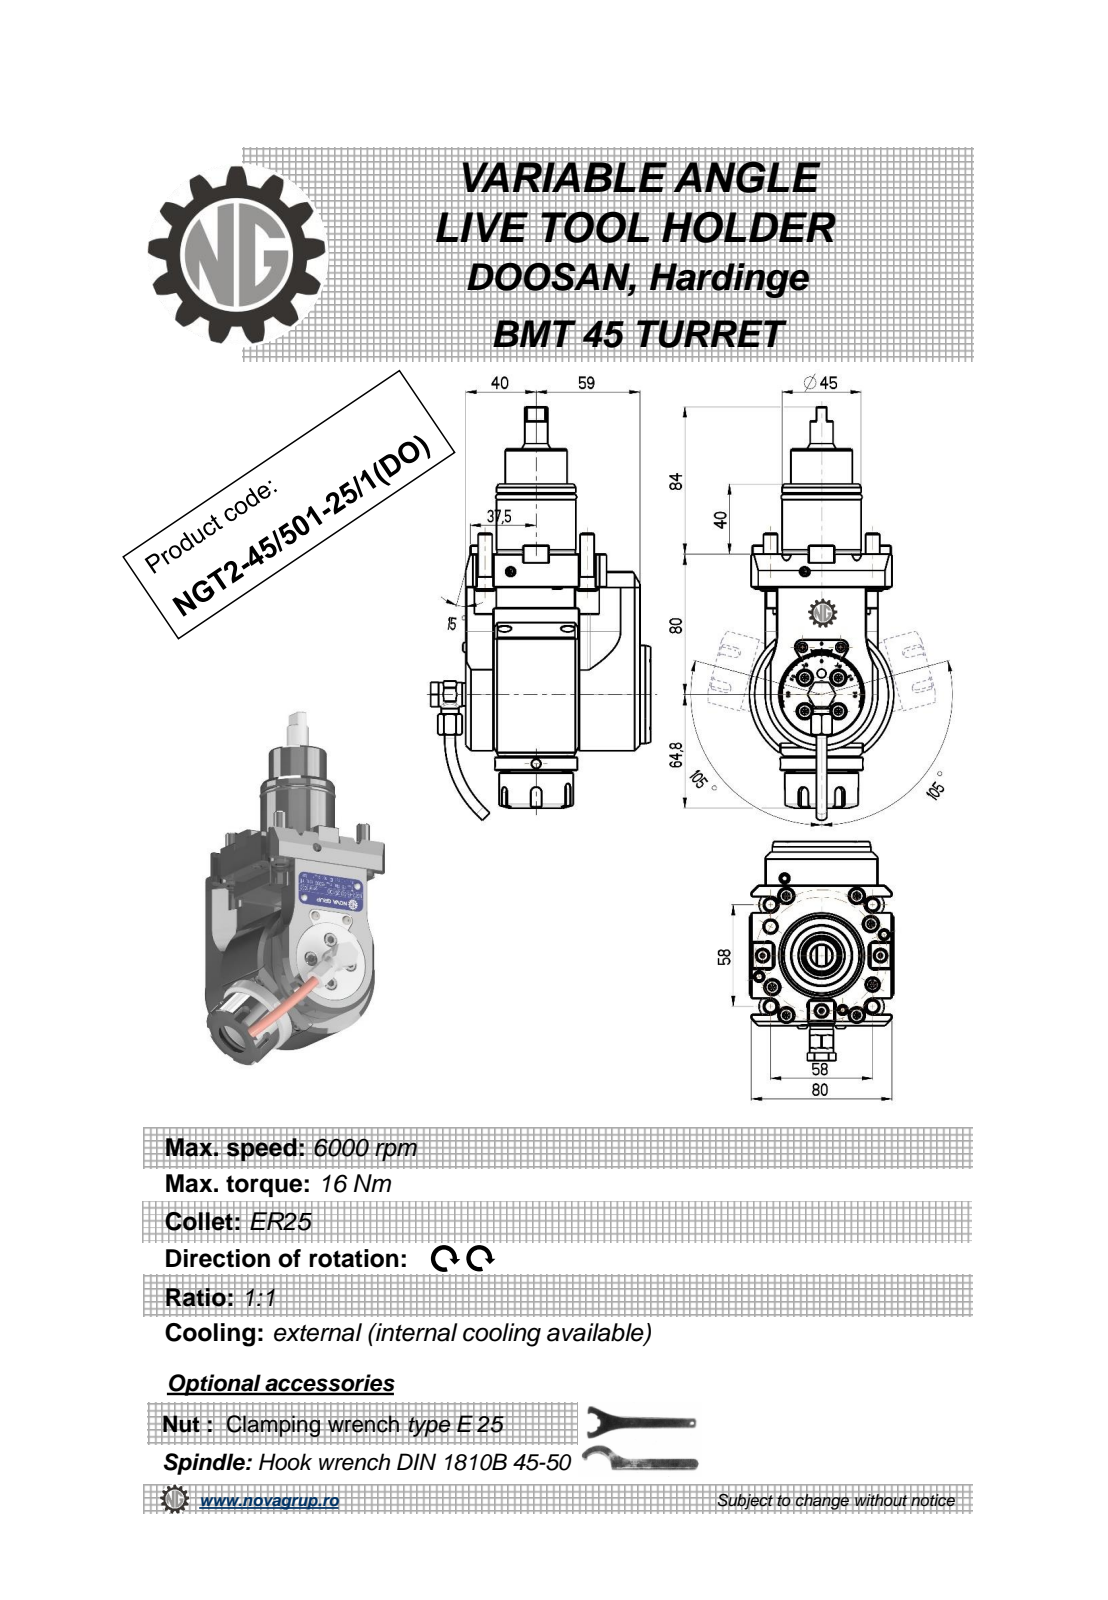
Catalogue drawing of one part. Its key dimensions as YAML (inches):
part_name: "NGT2_45_501_25_1_DO"
step_written_by: "PRO/ENGINEER BY PARAMETRIC TECHNOLOGY CORPORATION, 2010280 (CONFIG_CONTROL_DESIGN)"
units: inches
bodies: {solids: 2, faces: 655, planar: 293, cylindrical: 168, other: 194}
overall_size: [9.278, 4.917, 3.228]
volume: 49.88
surface_area: 135.7
round_holes:
  - {diameter: 0.157, count: 3}
  - {diameter: 0.197, count: 2}
  - {diameter: 0.268, count: 2}
  - {diameter: 0.118, count: 1}
  - {diameter: 0.244, count: 1}
  - {diameter: 0.354, count: 1}
  - {diameter: 0.433, count: 1}
  - {diameter: 0.799, count: 1}
  - {diameter: 1.654, count: 1}
  - {diameter: 1.661, count: 1}
round_bosses_or_shafts:
  - {diameter: 0.512, count: 6}
  - {diameter: 0.315, count: 4}
  - {diameter: 0.236, count: 4}
  - {diameter: 0.394, count: 2}
  - {diameter: 0.224, count: 2}
  - {diameter: 3.228, count: 1}
  - {diameter: 2.205, count: 1}
  - {diameter: 1.85, count: 1}
partial_cylinders:
  - {radius: 0.01, count: 20}
  - {radius: 0.118, count: 5}
  - {radius: 0.02, count: 4}
  - {radius: 0.177, count: 4}
  - {radius: 0.276, count: 4}
  - {radius: 0.031, count: 2}
  - {radius: 0.039, count: 2}
  - {radius: 0.197, count: 2}
face_to_face_distances: [2.52, 1.22, 0.315, 0.236, 0.63, 3.898, 1.378, 4.134, 1.614, 0.354]
hole_center_spacings: [1.314, 0.016, 1.553, 1.715, 1.727, 1.929, 1.945, 2.627]
